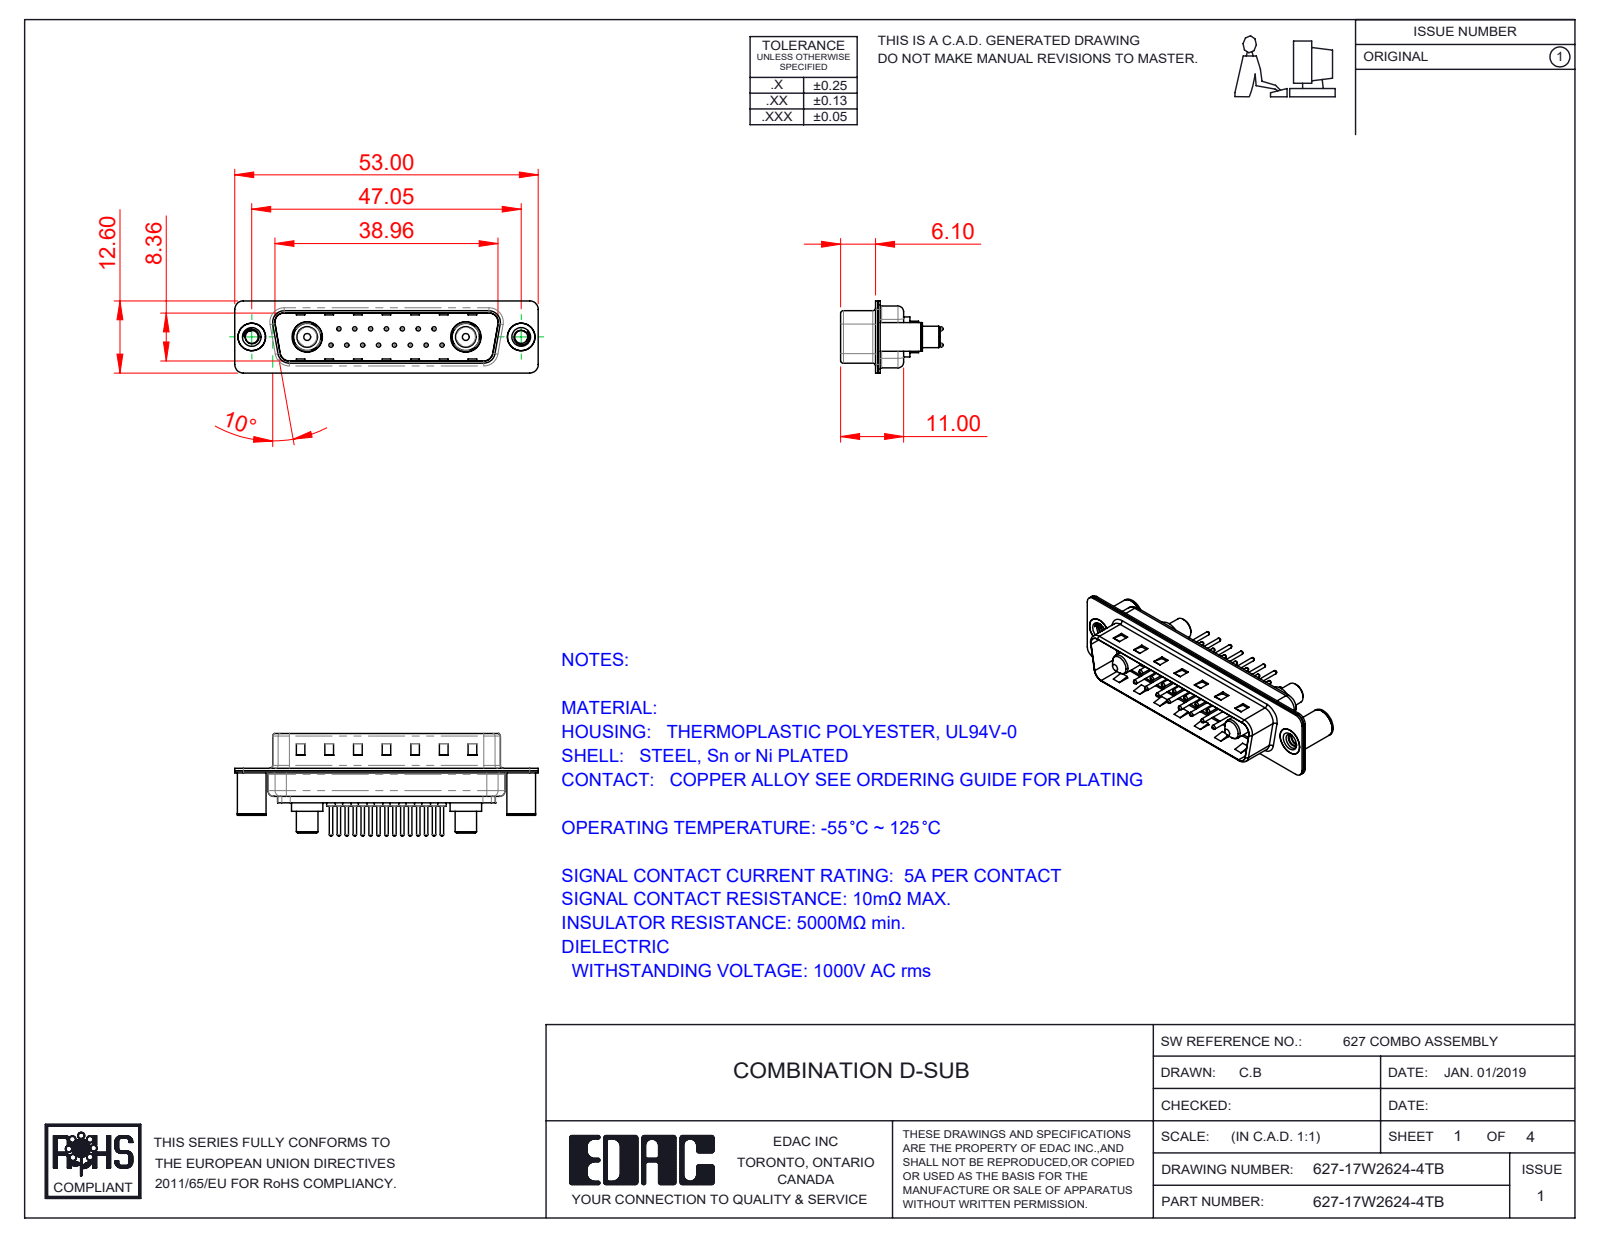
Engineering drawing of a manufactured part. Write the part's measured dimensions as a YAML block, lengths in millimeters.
part_name: "627Combo Contact Row 1_24; 627Combo Contact Row 2_24; Power Pin_40A S; 627Combo Threaded Board Spacer_3 (+5 more)"
step_written_by: "SolidWorks 2016 (CONFIG_CONTROL_DESIGN)"
units: millimeters
bodies: {solids: 24, faces: 1049, planar: 296, cylindrical: 413, other: 340}
overall_size: [53, 17.9, 12.6]
volume: 3018
surface_area: 7066
round_holes:
  - {diameter: 0.75, count: 15}
  - {diameter: 1.6, count: 15}
  - {diameter: 2, count: 15}
  - {diameter: 2.26, count: 2}
  - {diameter: 3.26, count: 2}
  - {diameter: 4, count: 2}
  - {diameter: 4.8, count: 2}
  - {diameter: 4.85, count: 2}
  - {diameter: 5.3, count: 2}
round_bosses_or_shafts:
  - {diameter: 1.5, count: 15}
  - {diameter: 0.6, count: 15}
  - {diameter: 5.5, count: 2}
  - {diameter: 5.2, count: 2}
  - {diameter: 5, count: 2}
  - {diameter: 4.9, count: 2}
  - {diameter: 4.75, count: 2}
  - {diameter: 3.75, count: 2}
partial_cylinders:
  - {radius: 1.5, count: 16}
  - {radius: 2, count: 12}
  - {radius: 0.5, count: 8}
  - {radius: 1.6, count: 8}
  - {radius: 0.25, count: 4}
  - {radius: 0.6, count: 4}
  - {radius: 0.65, count: 4}
  - {radius: 0.9, count: 4}
face_to_face_distances: [0.4, 0.82, 9.58, 8.76, 1.5, 5.6, 5.2, 0.8, 1.22, 9.98]
hole_center_spacings: [3.16, 2.77, 5.54, 8.31, 5.04, 7.49, 11.08, 5.03]
